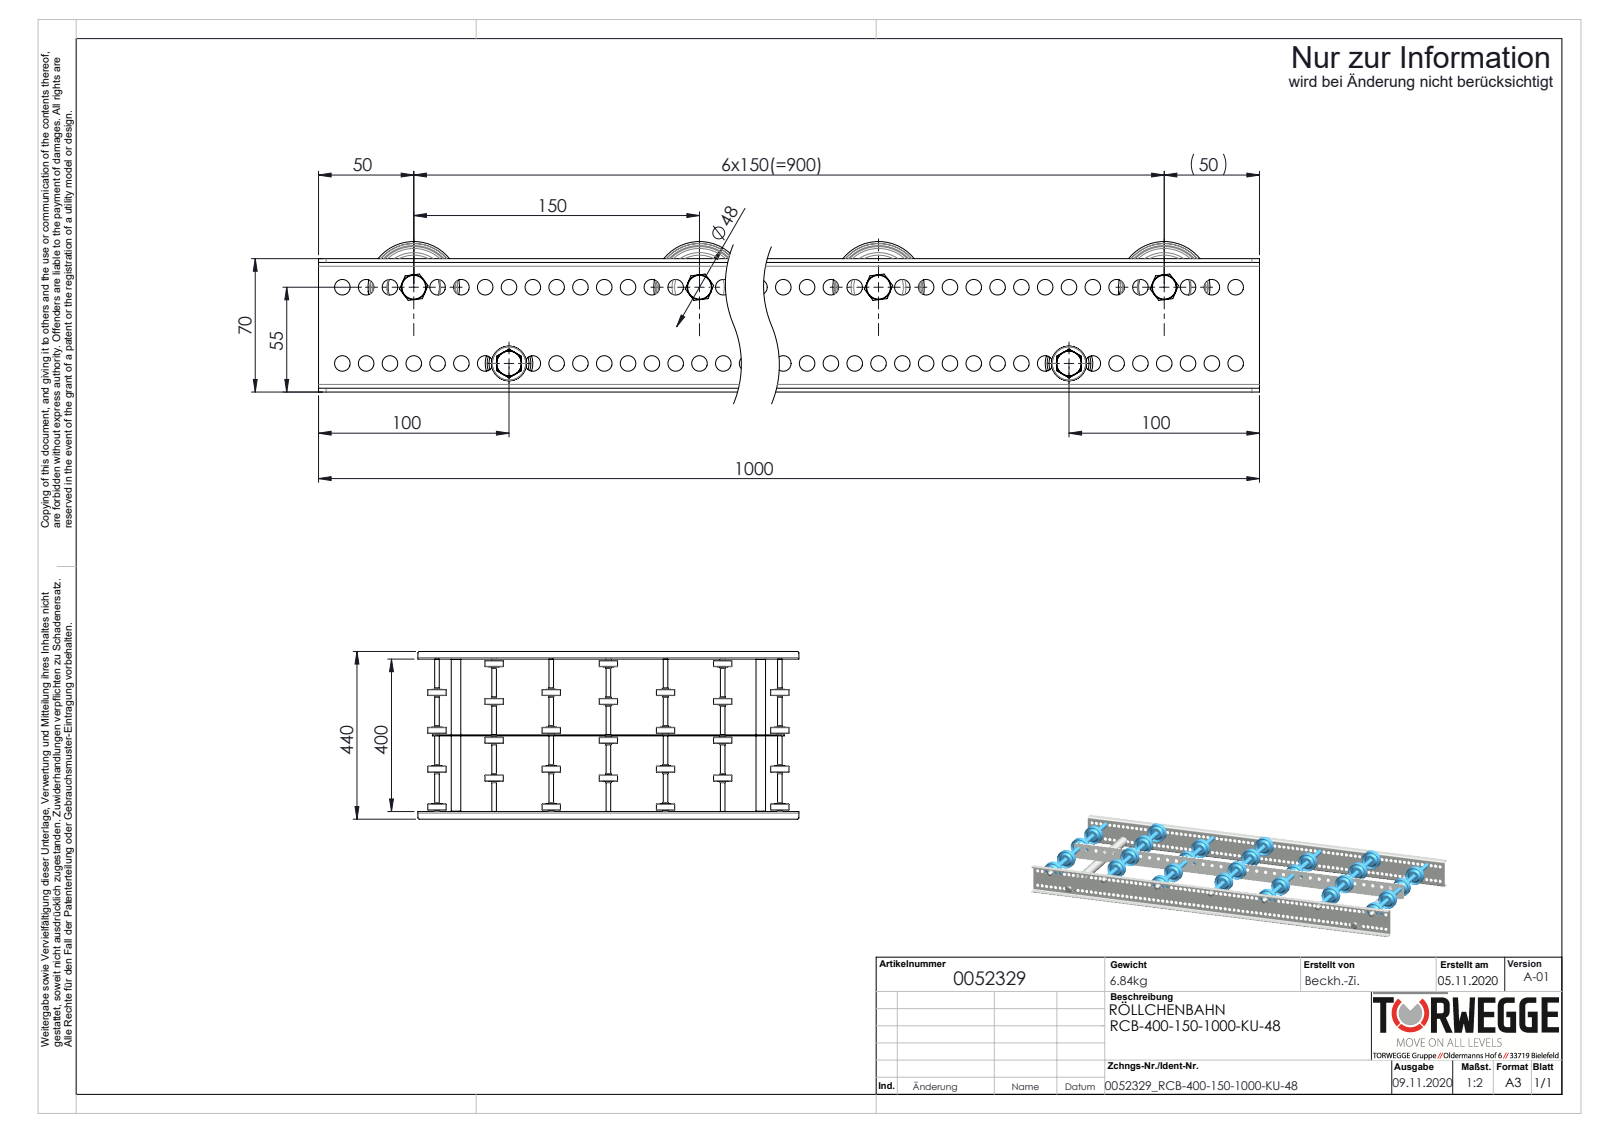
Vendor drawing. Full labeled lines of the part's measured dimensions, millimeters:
Part name (STEP PRODUCT): 0011532_2300-48-8; 0046278_KB-ROHR-12X1,75mm_KFG_L75,5; Profil_LRB-20x70x20x2_KFG_S100200_U-PROFIL-20-70-20-2-LRB-L=1000; Hutmutter_DIN_1587_M8 (+6 more)
STEP written by: SolidWorks 2020 (AUTOMOTIVE_DESIGN)
Units: millimetres
Bodies: 90 solids, 3544 faces (616 planar, 1452 cylindrical, 1476 other)
Overall size (bounding box): 1000 × 440 × 79
Volume: 1 394 000 mm³ · Surface area: 1 115 000 mm²
Round holes (diameter × count): ⌀8.2 ×158, ⌀8.5 ×37, ⌀6.65 ×7, ⌀9.65 ×7, ⌀13.7 ×7, ⌀6.8 ×2, ⌀21 ×2
Round bosses / shafts (diameter × count): ⌀8 ×9, ⌀48 ×7, ⌀27 ×7, ⌀12.7 ×7, ⌀12.5 ×7, ⌀12 ×7, ⌀25 ×2
Partial cylindrical surfaces — rounded edges, fillets, slot ends (radius × count): R4 ×8, R2 ×4, R5 ×4
Main face-to-face distances: 2, 402, 68, 404, 400, 201.1, 198.6, 200.9, 198.9, 203.1
Hole centre spacings: 12.5, 25, 37.5, 50, 62.5, 75, 87.5, 100
